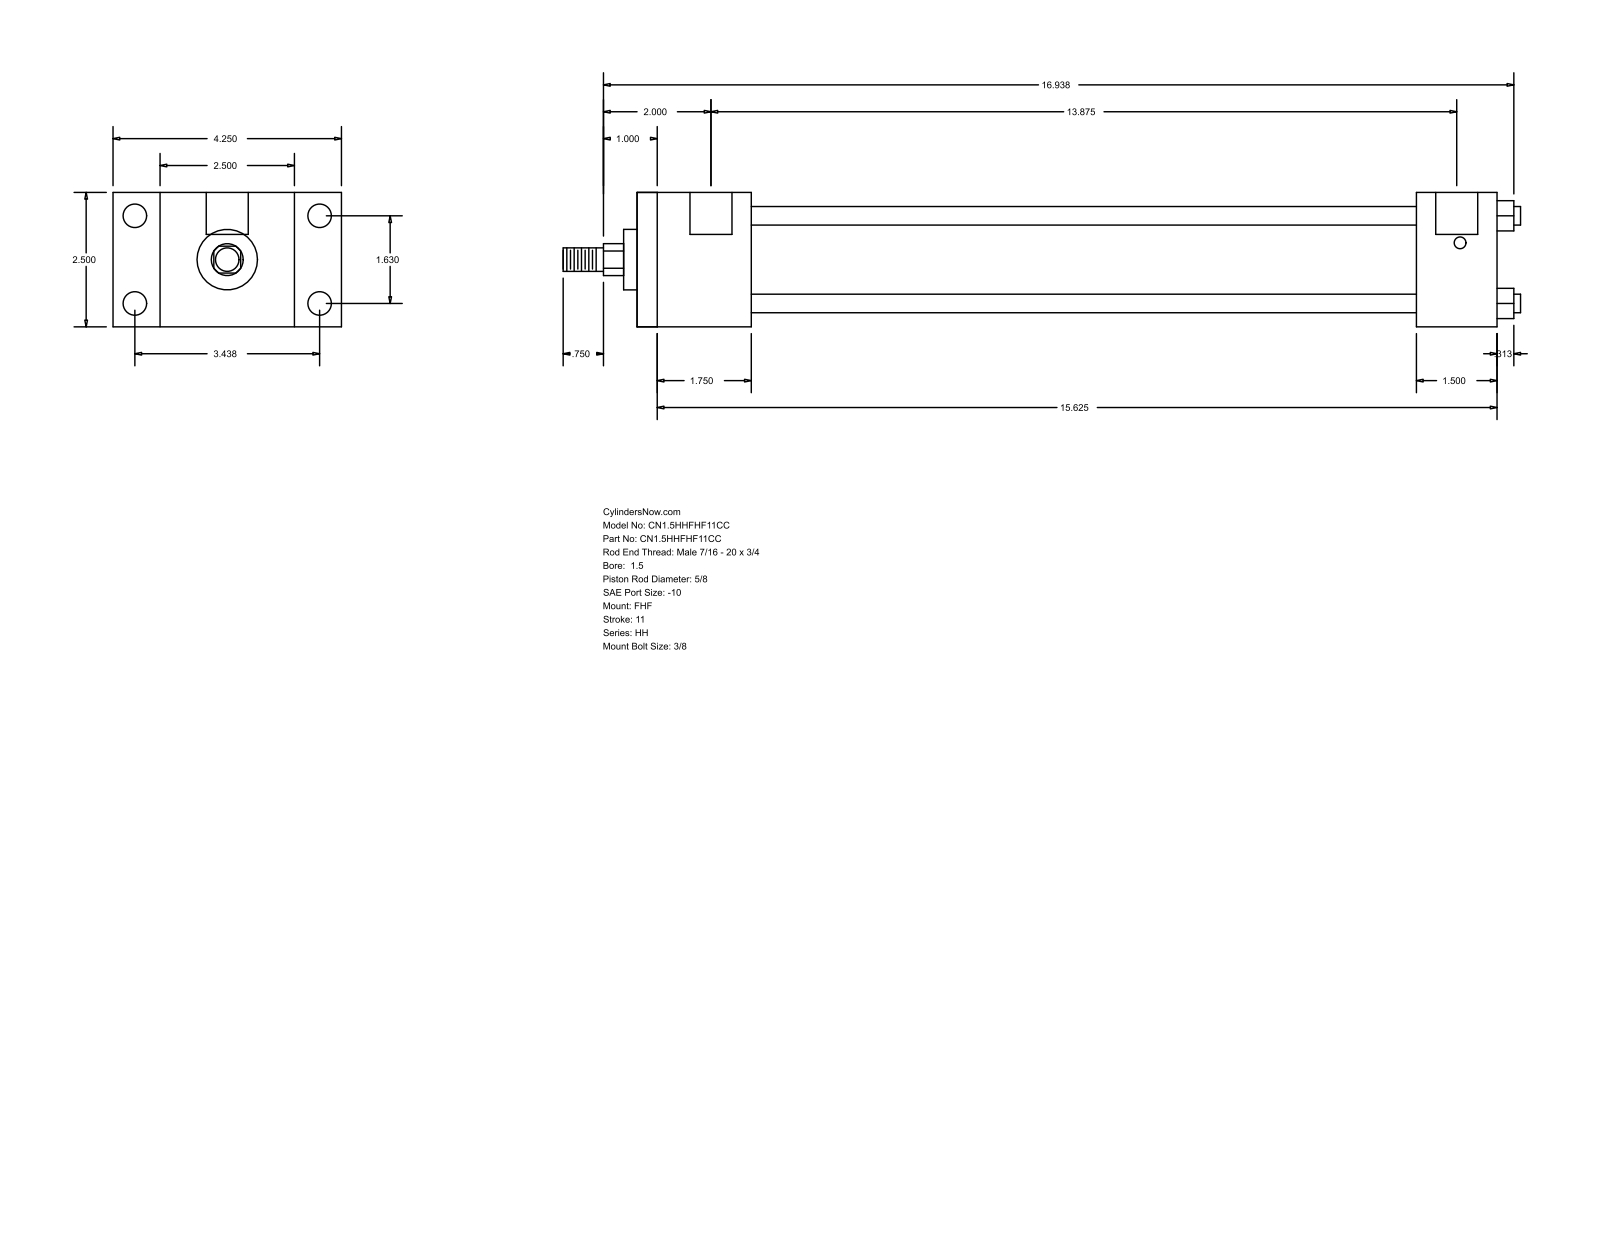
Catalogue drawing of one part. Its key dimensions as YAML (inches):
part_name: "HH_FHF__0150_0.625"
step_written_by: "GSSL Pune (CONFIG_CONTROL_DESIGN)"
units: inches
bodies: {solids: 0, faces: 88, planar: 60, cylindrical: 28, other: 0}
overall_size: [17.813, 4.25, 2.5]
round_holes:
  - {diameter: 0.219, count: 4}
  - {diameter: 0.438, count: 4}
  - {diameter: 0.781, count: 2}
round_bosses_or_shafts:
  - {diameter: 0.345, count: 4}
  - {diameter: 1.75, count: 1}
  - {diameter: 1.125, count: 1}
  - {diameter: 0.625, count: 1}
  - {diameter: 0.437, count: 1}
partial_cylinders:
  - {radius: 0.297, count: 1}
face_to_face_distances: [2.5, 0.875, 3.375, 2.125, 4.25, 16, 13.875, 14.5, 12.375, 1.5]
hole_center_spacings: [1.63, 3.438, 3.805, 14, 0.062, 0.063, 13.875, 13.937]
